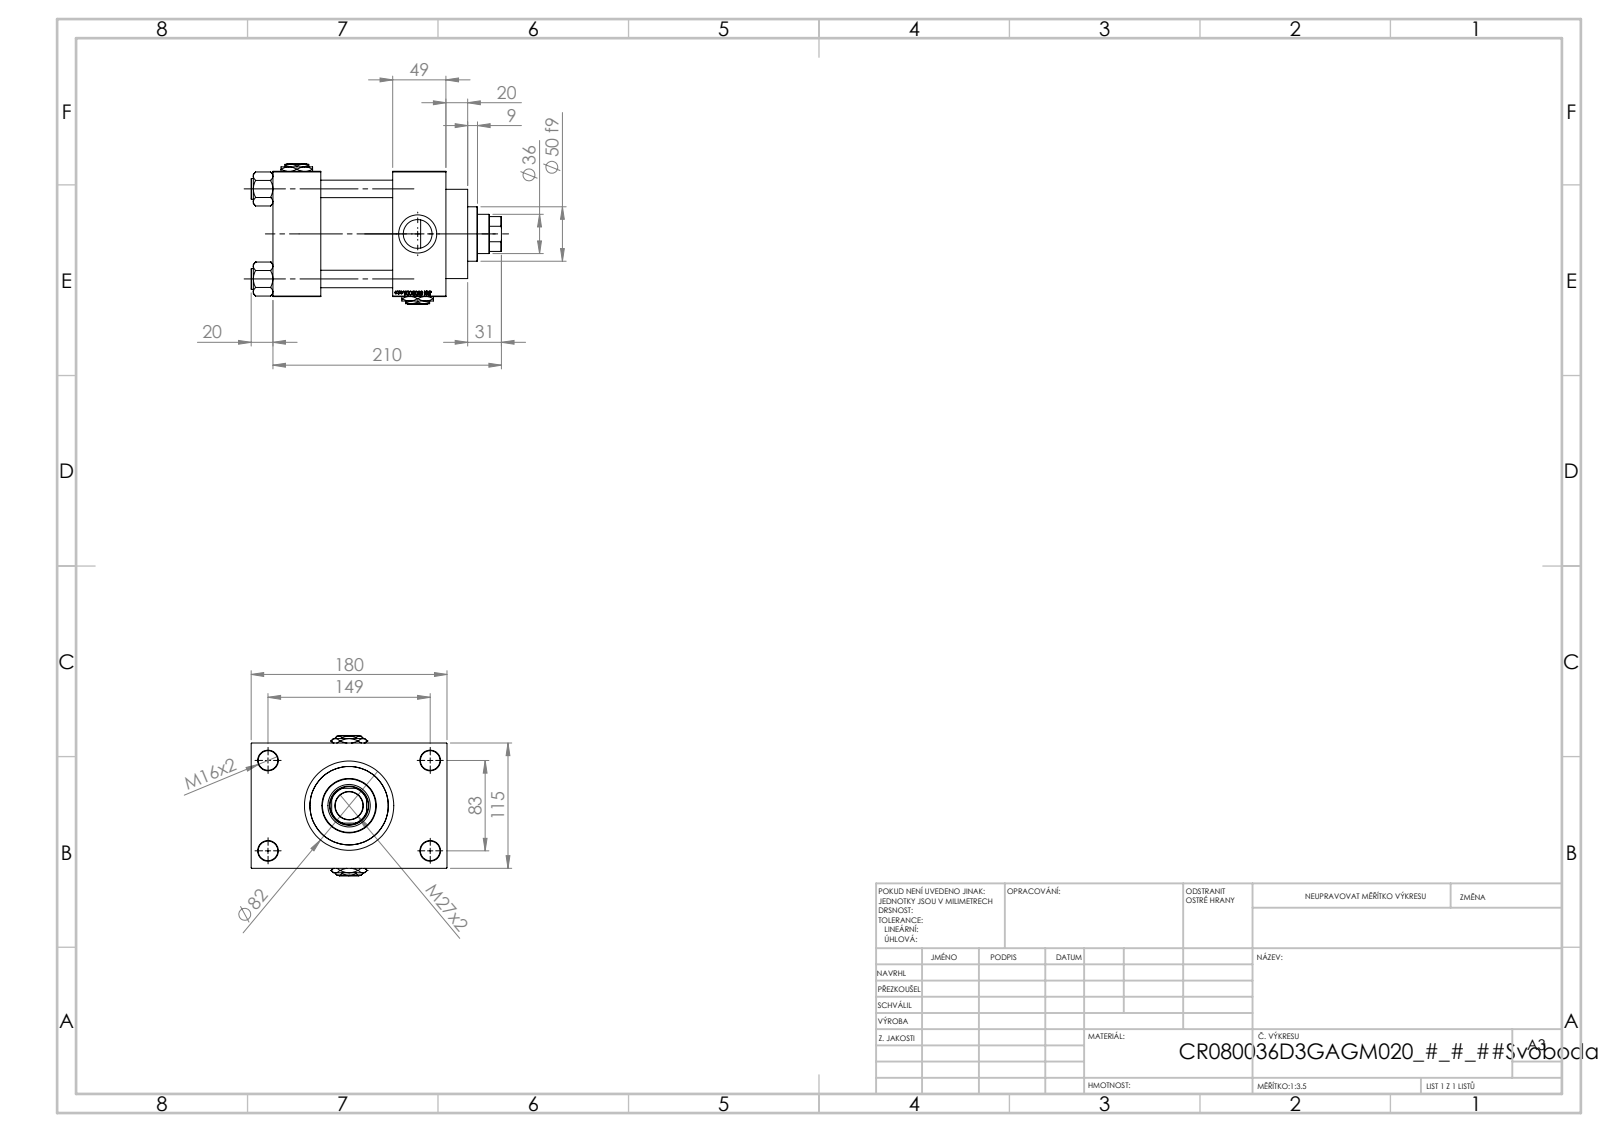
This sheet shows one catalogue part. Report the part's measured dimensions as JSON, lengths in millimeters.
{"part_name": "V215CR_VCP_D; V215CR_D_Body; Zatka_pro_OIL_PORT; NUT_M5_D (+2 more)", "step_written_by": "SolidWorks 2019 (CONFIG_CONTROL_DESIGN)", "units": "millimeters", "bodies": {"solids": 13, "faces": 1242, "planar": 591, "cylindrical": 93, "other": 558}, "overall_size": [230, 180, 129], "volume_mm3": 1973000, "surface_area_mm2": 301542, "round_holes": [[16, 4], [18, 4], [26.44, 3], [35, 3], [7, 2], [25.5, 1], [36, 1], [39, 1], [61, 1], [72, 1], [80, 1]], "round_bosses_or_shafts": [[19, 4], [86, 1], [82, 1], [50, 1]], "partial_cylinders_radius": [[17.5, 1]], "face_to_face_distances": [115, 66, 110, 49, 44, 159, 147.5, 32.5, 20, 69], "hole_center_spacings": [33.15, 58.48, 82.7, 85.28, 89.24, 115.85, 142.43, 83]}
